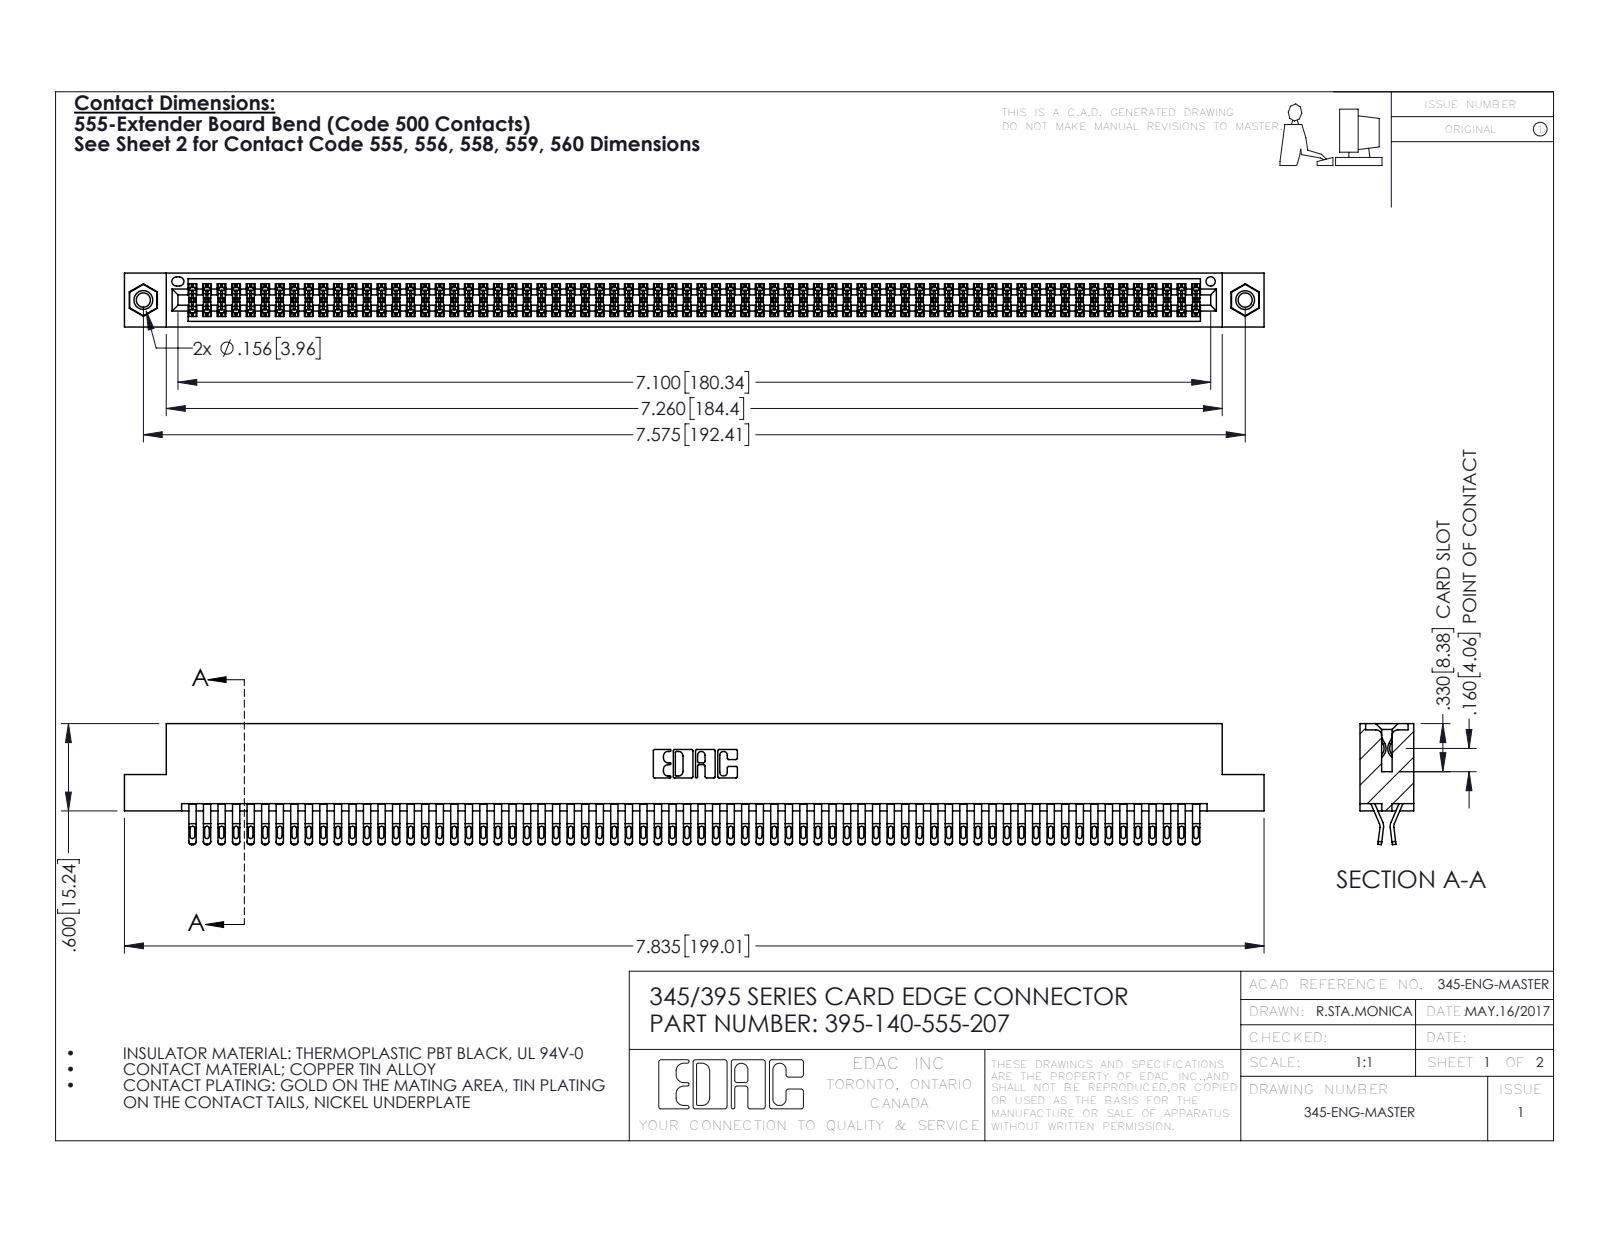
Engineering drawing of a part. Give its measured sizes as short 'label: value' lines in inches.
name: 345-292-001_555 Tail; 345-250-001_345-250-005-103; 345 Part_Flush Mounting Lugs - 0.156 Dia-TI; 395-140-555-207
written by: SolidWorks 2016 (CONFIG_CONTROL_DESIGN)
unit: in
bodies: 143 solids, 8026 faces (4452 planar, 3558 cylindrical, 16 other)
size: 7.835 × 0.832 × 0.37
volume: 1.22 in³; area: 48.86 in²
holes: 2× ⌀0.098, 2× ⌀0.125, 2× ⌀0.156, 1× ⌀0.064
bosses: 2× ⌀0.155
rounds: 350× R0.016, 280× R0.02, 210× R0.006, 22× R0.01, 6× R0.007, 6× R0.031, 3× R0.026, 2× R0.01
face distances: 0.072, 0.298, 0.025, 0.37, 0.2, 0.098, 0.272, 0.225, 0.175, 0.149
hole spacings: 0.27, 7.339, 7.575
